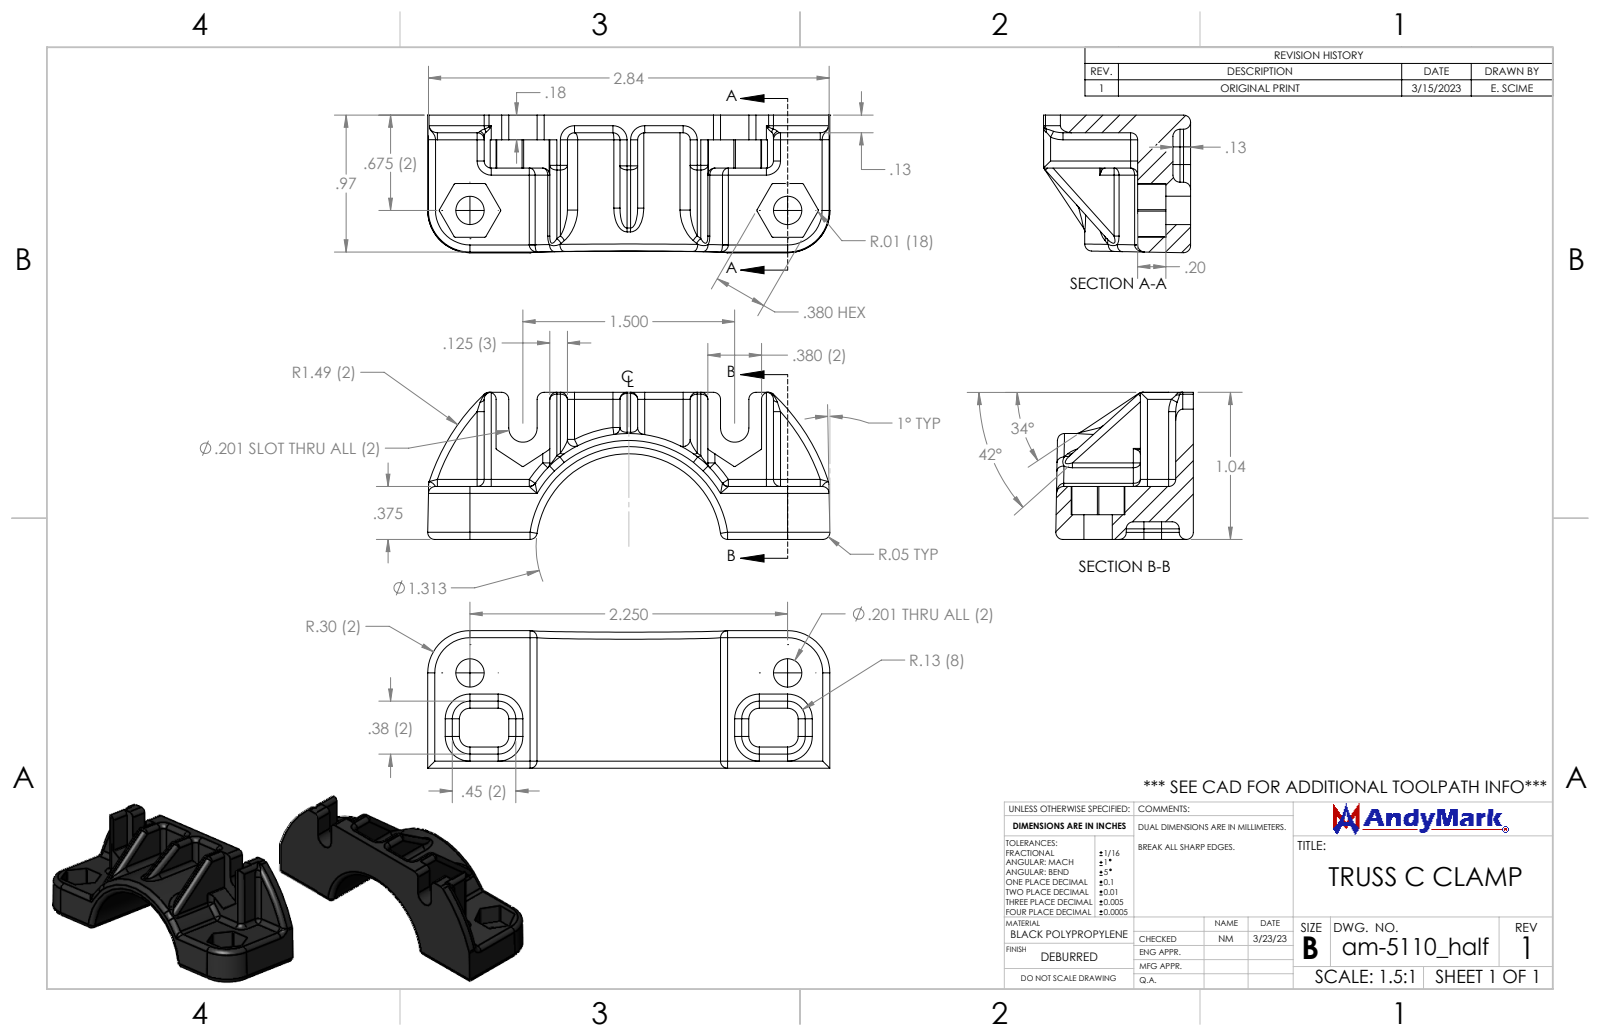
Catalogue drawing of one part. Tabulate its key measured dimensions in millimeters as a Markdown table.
| quantity | value |
| --- | --- |
| part name | am-5110_half Pipe Clamp |
| STEP written by | SolidWorks 2022 (AUTOMOTIVE_DESIGN) |
| units | millimeters |
| bodies | 1 solid, 366 faces (64 planar, 160 cylindrical, 142 other) |
| overall size | 72.4 × 26.3 × 24.8 |
| volume | 15 500 mm³ |
| surface area | 8 252 mm² |
| round holes (diameter × count) | 5.1 × 2 |
| partial cylindrical surfaces (radius × count) | 1 × 76, 0.3 × 45, 1.3 × 2, 2.6 × 2, 3.2 × 2, 16.7 × 1, 20.3 × 1, 37.8 × 1 |
| main face-to-face distances | 9.5, 21.7, 21.1, 3.2, 6.4, 46.6, 24.9, 1.3, 9.6, 12.1 |
| hole center spacings | 57.2 |
